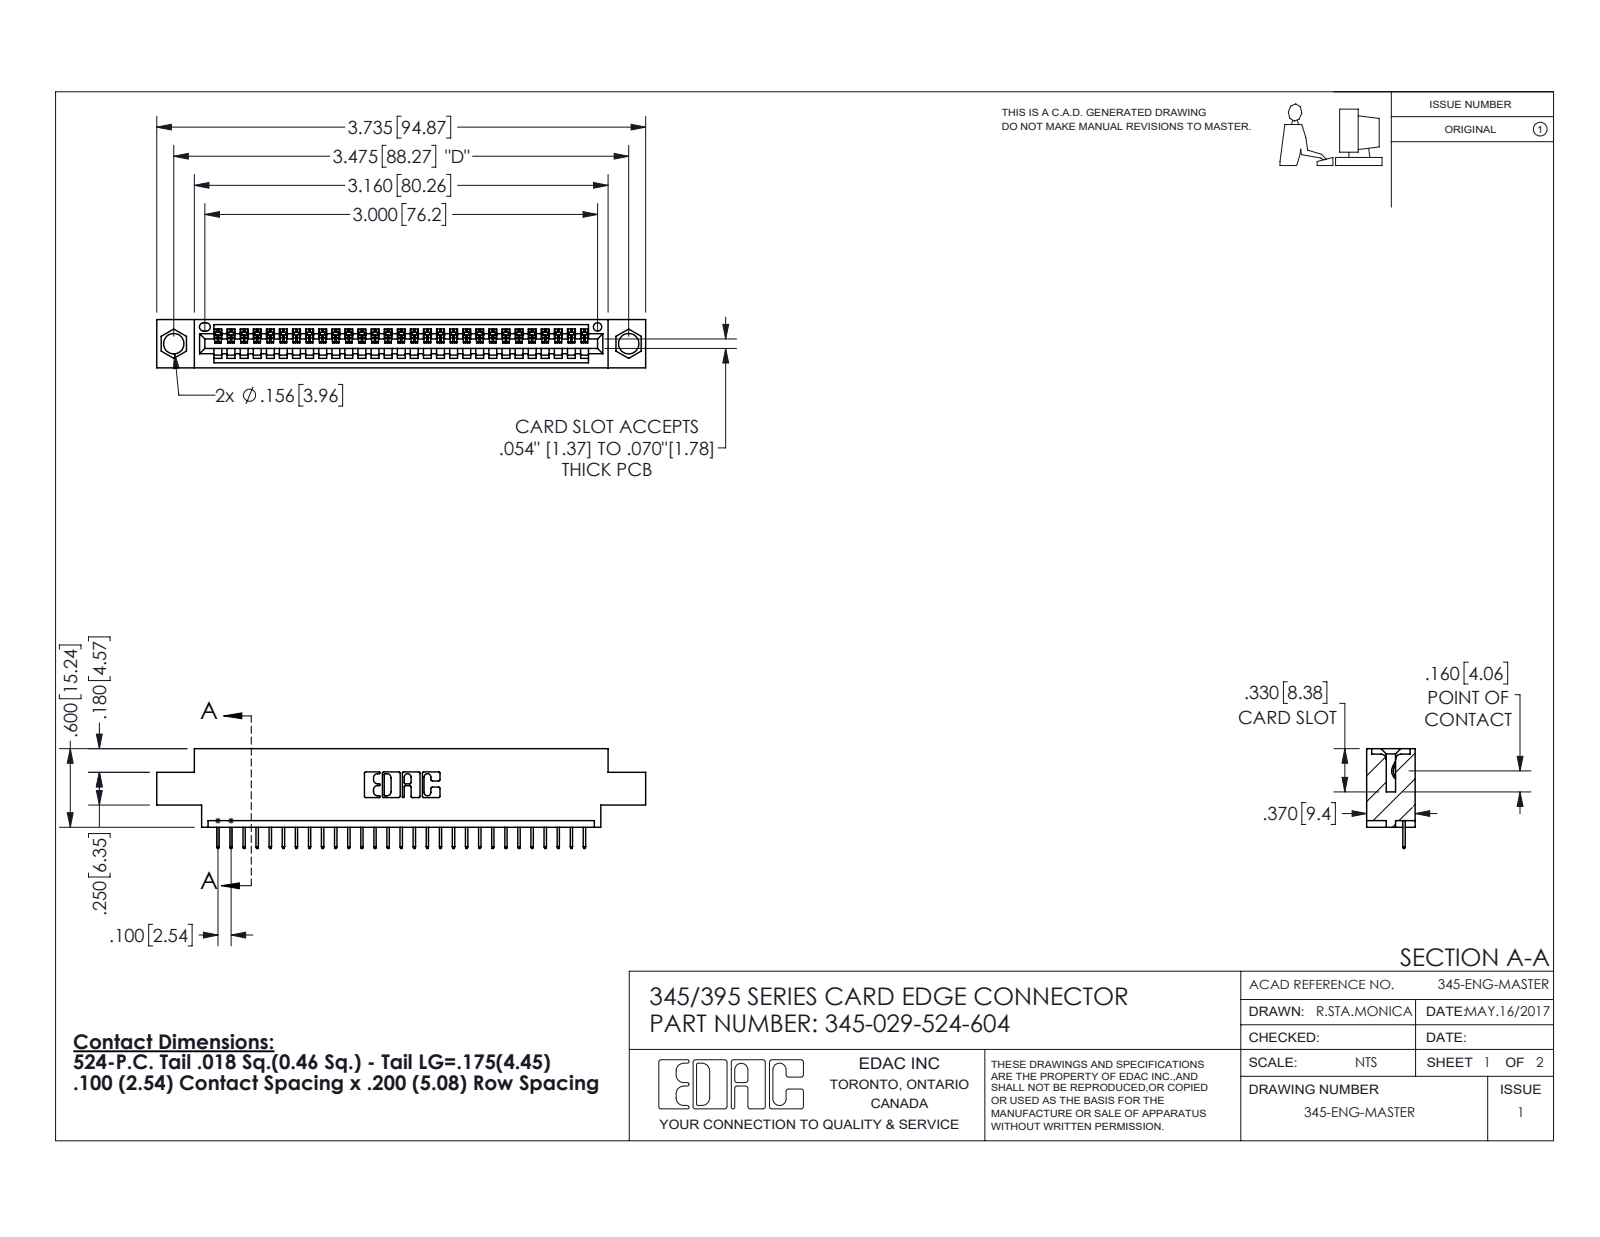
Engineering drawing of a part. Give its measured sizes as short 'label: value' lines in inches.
name: 345 Part_0.170 Offset - 0.156 Dia-TH; 345-029-524-604; 345-292-001_345-293-124
written by: SolidWorks 2016 (CONFIG_CONTROL_DESIGN)
unit: in
bodies: 30 solids, 1928 faces (1418 planar, 510 cylindrical, 0 other)
size: 3.735 × 0.762 × 0.37
volume: 0.524 in³; area: 16.75 in²
holes: 2× ⌀0.156, 1× ⌀0.064
rounds: 58× R0.006, 22× R0.01, 6× R0.007, 6× R0.031, 3× R0.026, 2× R0.031, 2× R0.04, 1× R0.014
face distances: 0.072, 0.298, 0.37, 0.2, 0.098, 0.272, 0.025, 0.225, 0.072, 0.175
hole spacings: 0.27, 3.24, 3.475
